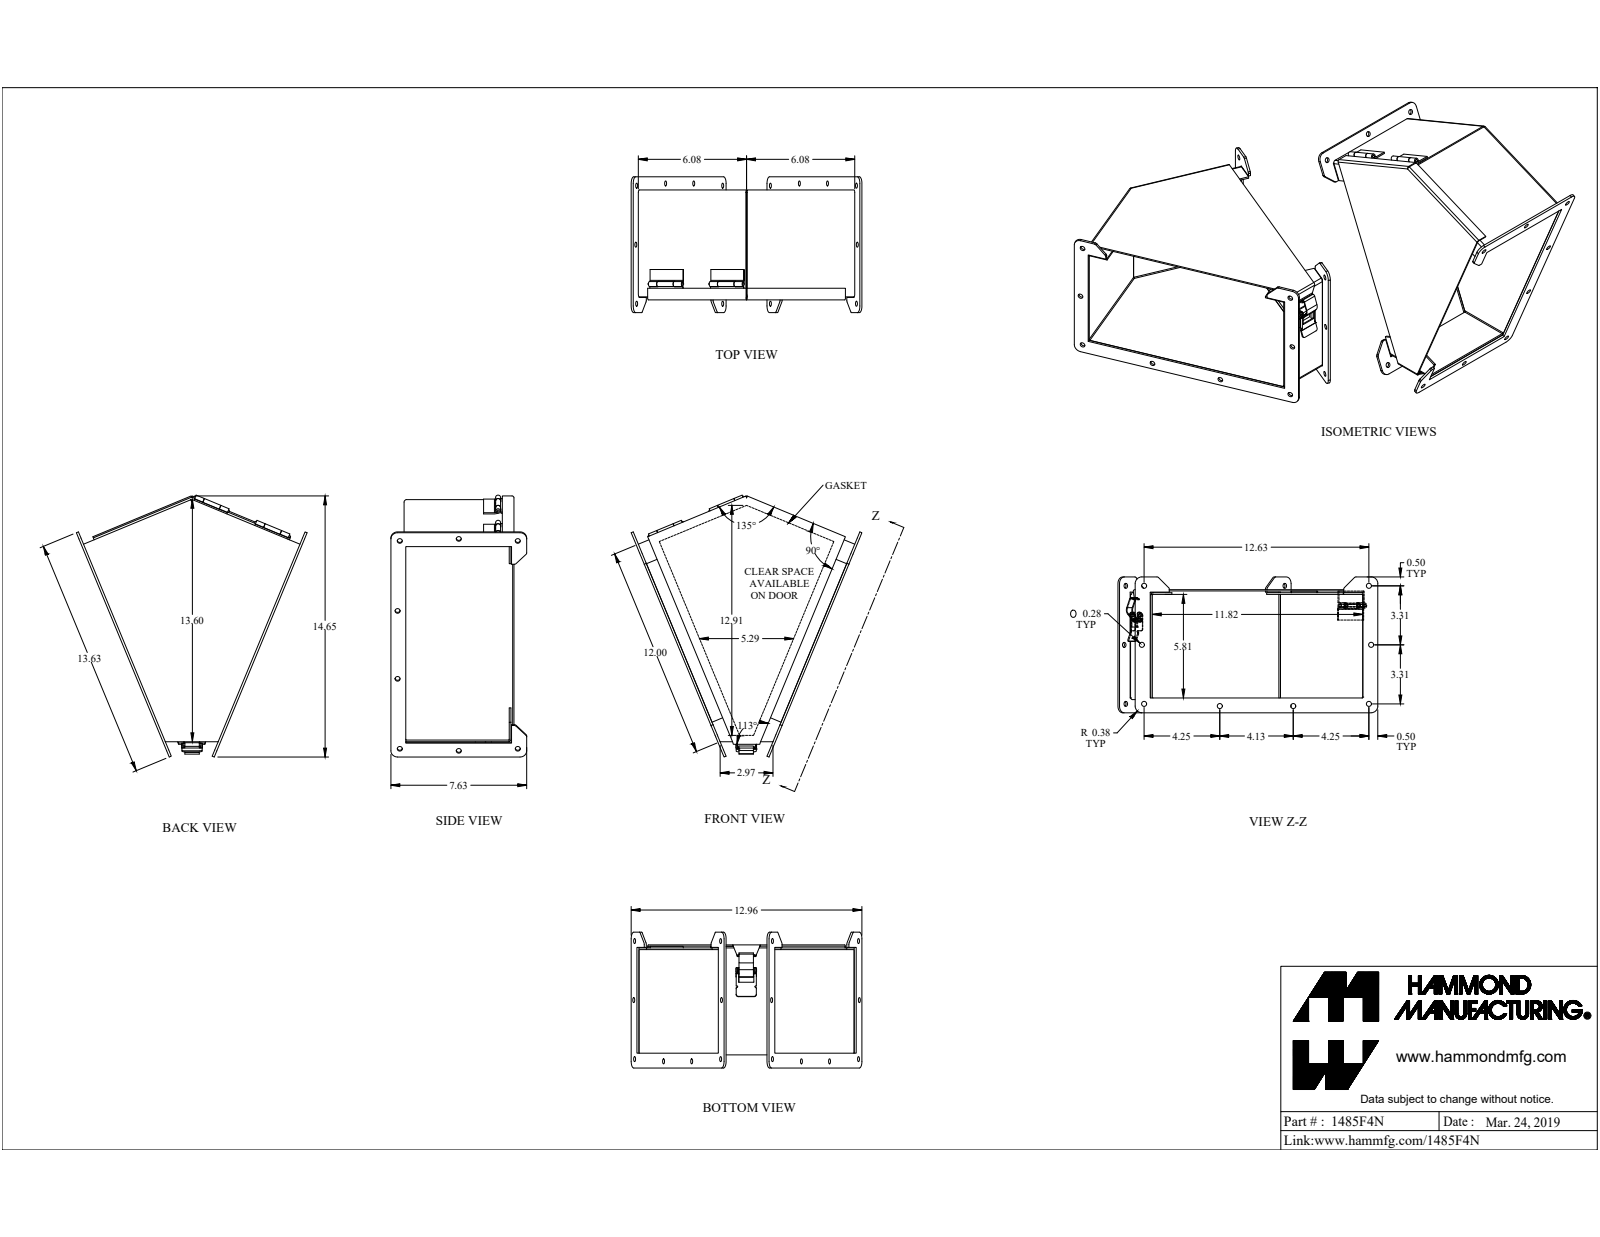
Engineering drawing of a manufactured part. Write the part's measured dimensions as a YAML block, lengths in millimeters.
part_name: "1485F4N"
step_written_by: "SolidWorks 2019 (CONFIG_CONTROL_DESIGN)"
units: millimeters
bodies: {solids: 14, faces: 325, planar: 193, cylindrical: 118, other: 14}
overall_size: [373.4, 329.1, 193.7]
volume: 573500
surface_area: 503400
round_holes:
  - {diameter: 7.1, count: 16}
  - {diameter: 3.2, count: 4}
  - {diameter: 3.3, count: 1}
  - {diameter: 4.2, count: 1}
round_bosses_or_shafts:
  - {diameter: 7, count: 4}
  - {diameter: 4.7, count: 2}
  - {diameter: 3.2, count: 2}
  - {diameter: 4, count: 1}
  - {diameter: 3.2, count: 1}
partial_cylinders:
  - {radius: 3.2, count: 11}
  - {radius: 9.5, count: 8}
  - {radius: 0.4, count: 7}
  - {radius: 1.2, count: 6}
  - {radius: 3.6, count: 6}
  - {radius: 0.9, count: 4}
  - {radius: 2.7, count: 4}
  - {radius: 0.9, count: 3}
face_to_face_distances: [2.4, 1.8, 152.5, 154.9, 154.4, 156.8, 2.4, 150, 3.2, 3.2]
hole_center_spacings: [334.6, 28.1, 84.2, 84.2, 140.2, 168.3, 202.6, 232.9]
